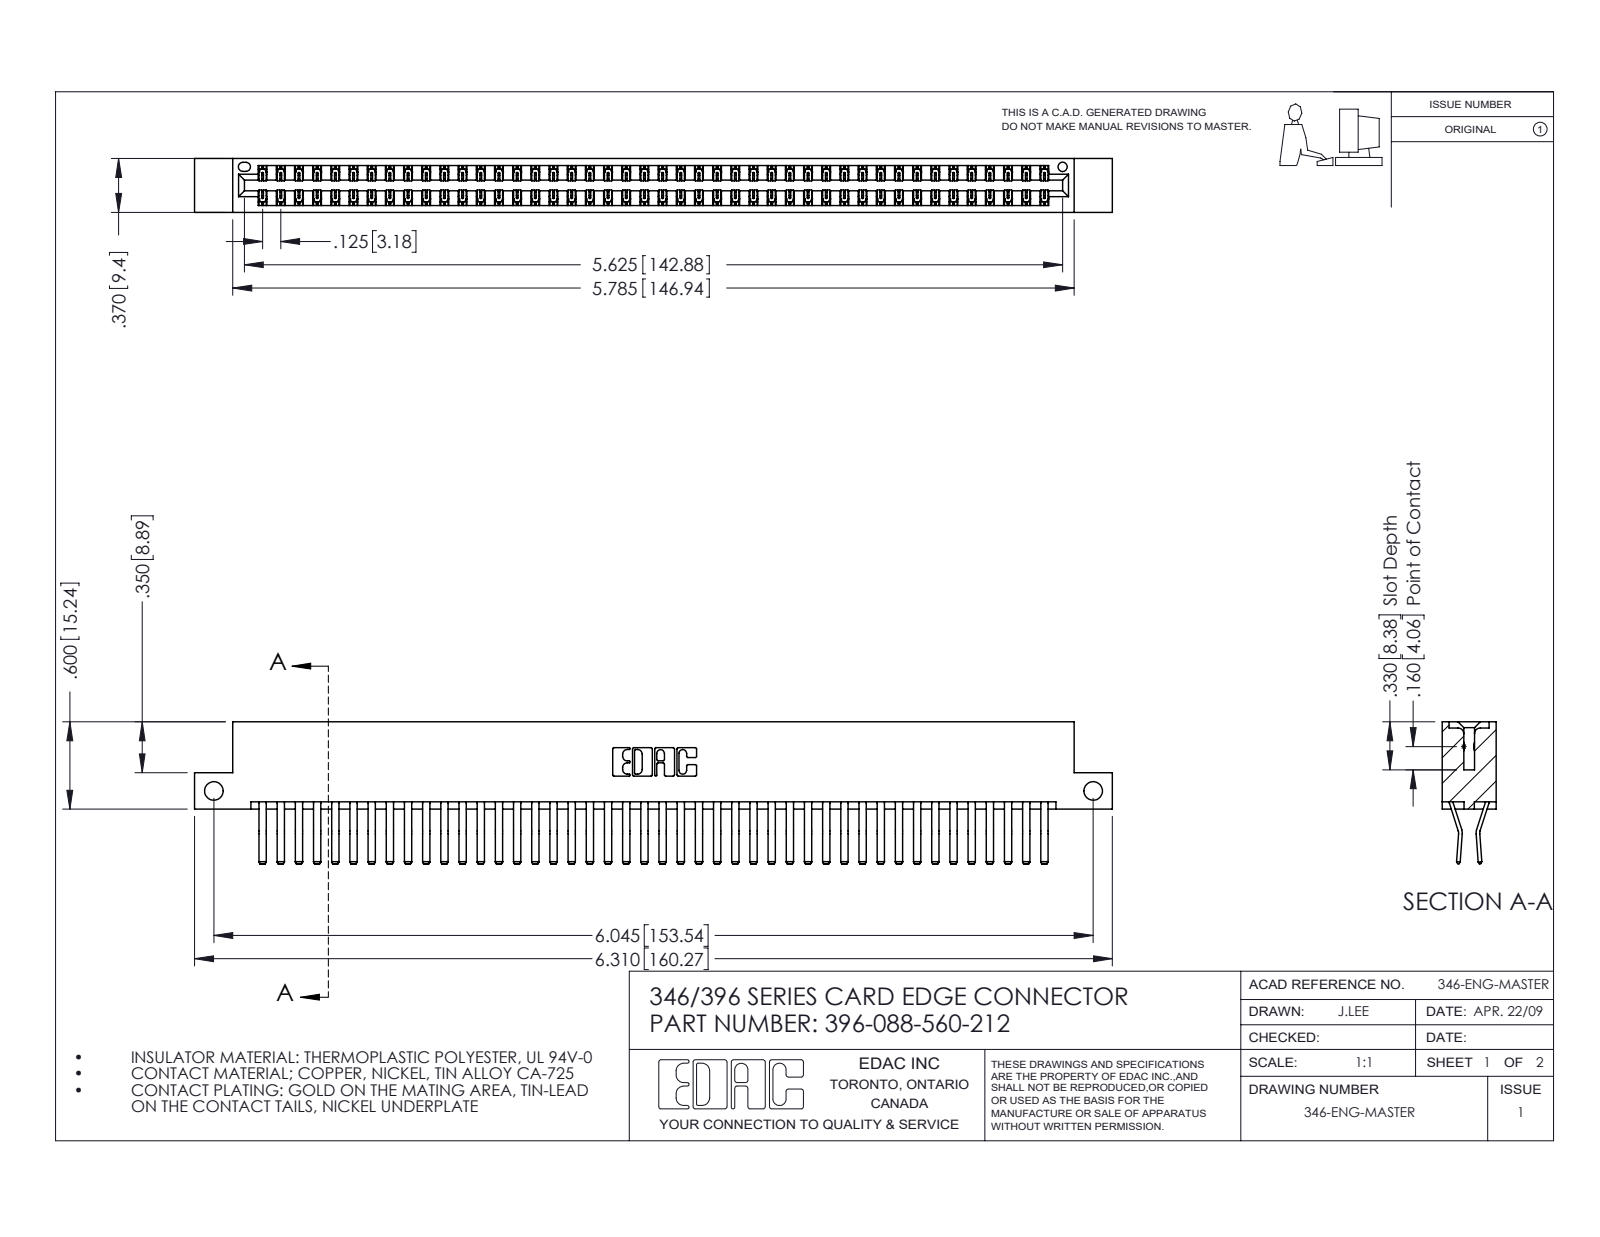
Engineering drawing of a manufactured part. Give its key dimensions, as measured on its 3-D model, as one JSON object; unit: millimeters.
{"part_name": "396-088-560-212; 345-292-001_560 Tail; 346 Part_Flush Mounting Lugs - Side Mount", "step_written_by": "SolidWorks 2016 (CONFIG_CONTROL_DESIGN)", "units": "millimeters", "bodies": {"solids": 89, "faces": 4874, "planar": 3156, "cylindrical": 1718, "other": 0}, "overall_size": [160.3, 24.8, 9.4], "volume_mm3": 16100, "surface_area_mm2": 23610, "round_holes": [[3.3, 2], [1.6, 1]], "partial_cylinders_radius": [[0.2, 132], [0.3, 22], [0.2, 6], [0.8, 6], [0.7, 3], [0.3, 2], [0.4, 2], [0.6, 2]], "face_to_face_distances": [1.2, 8.2, 9.4, 0.6, 6.4, 1.8, 7.6, 7, 3.8, 5.6], "hole_center_spacings": [153.5]}
